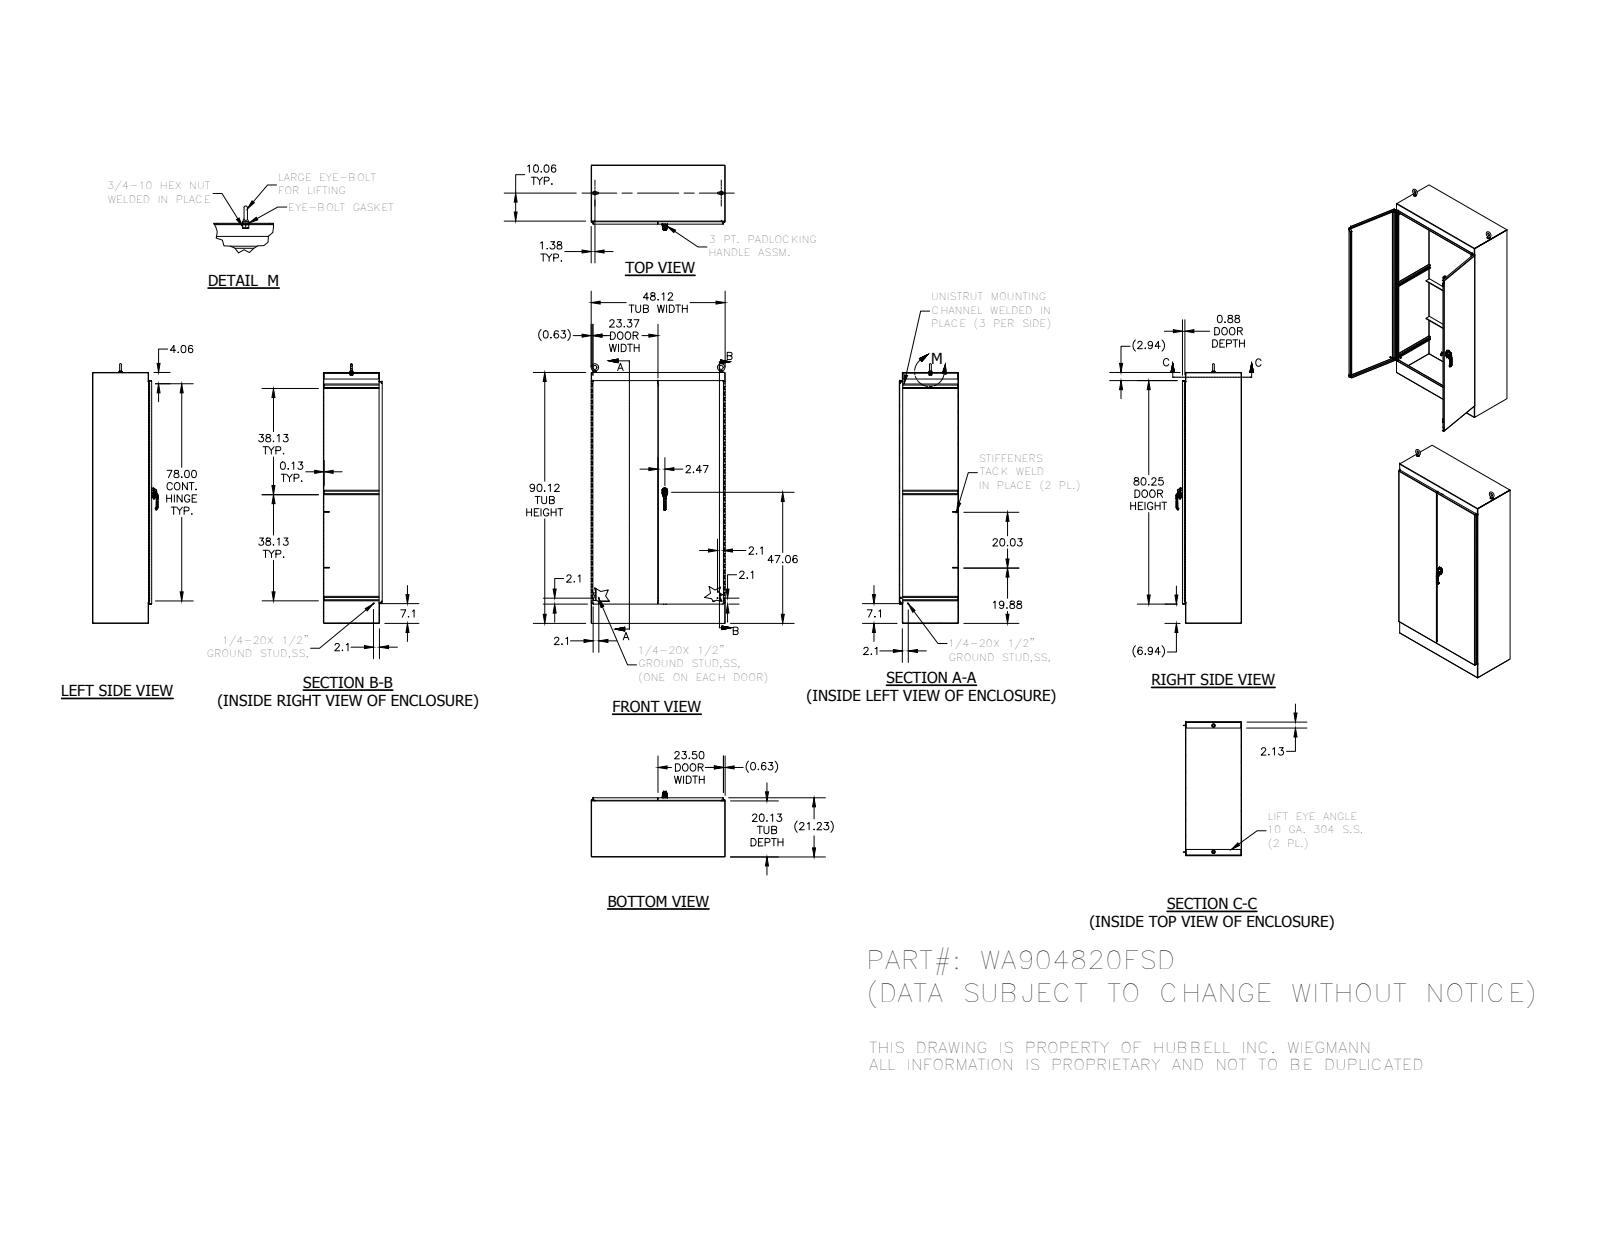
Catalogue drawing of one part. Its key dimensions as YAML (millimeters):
part_name: "FUN00102; HFW3025; 316298; 349132 (+8 more)"
step_written_by: "Autodesk Inventor 2014 (AUTOMOTIVE_DESIGN)"
units: millimeters
bodies: {solids: 66, faces: 3742, planar: 1767, cylindrical: 1237, other: 738}
overall_size: [2368.49, 1222.49, 596.85]
volume: 34330000
surface_area: 21770000
round_holes:
  - {diameter: 9.52, count: 16}
  - {diameter: 7.02, count: 8}
  - {diameter: 5.08, count: 4}
  - {diameter: 5.4, count: 3}
  - {diameter: 6, count: 3}
  - {diameter: 7.11, count: 3}
  - {diameter: 3.61, count: 2}
  - {diameter: 4.57, count: 2}
  - {diameter: 6.13, count: 2}
  - {diameter: 6.35, count: 2}
  - {diameter: 6.41, count: 2}
  - {diameter: 10.16, count: 2}
round_bosses_or_shafts:
  - {diameter: 8.56, count: 3}
  - {diameter: 6.35, count: 3}
  - {diameter: 31.75, count: 2}
  - {diameter: 28.45, count: 2}
  - {diameter: 25.4, count: 2}
  - {diameter: 19.05, count: 2}
  - {diameter: 14.29, count: 2}
  - {diameter: 13.37, count: 2}
partial_cylinders:
  - {radius: 0.5, count: 166}
  - {radius: 0.3, count: 89}
  - {radius: 0.79, count: 24}
  - {radius: 3.97, count: 21}
  - {radius: 3.17, count: 20}
  - {radius: 0.47, count: 19}
  - {radius: 0.25, count: 16}
  - {radius: 2, count: 15}
face_to_face_distances: [3.18, 3.17, 536.06, 532.88, 539.23, 536.05, 1219.2, 1216.02, 2286, 1222.38]
hole_center_spacings: [220.13, 660.4, 440.27, 1189.09, 1199.24, 880.53, 1248.73, 1286.95]
